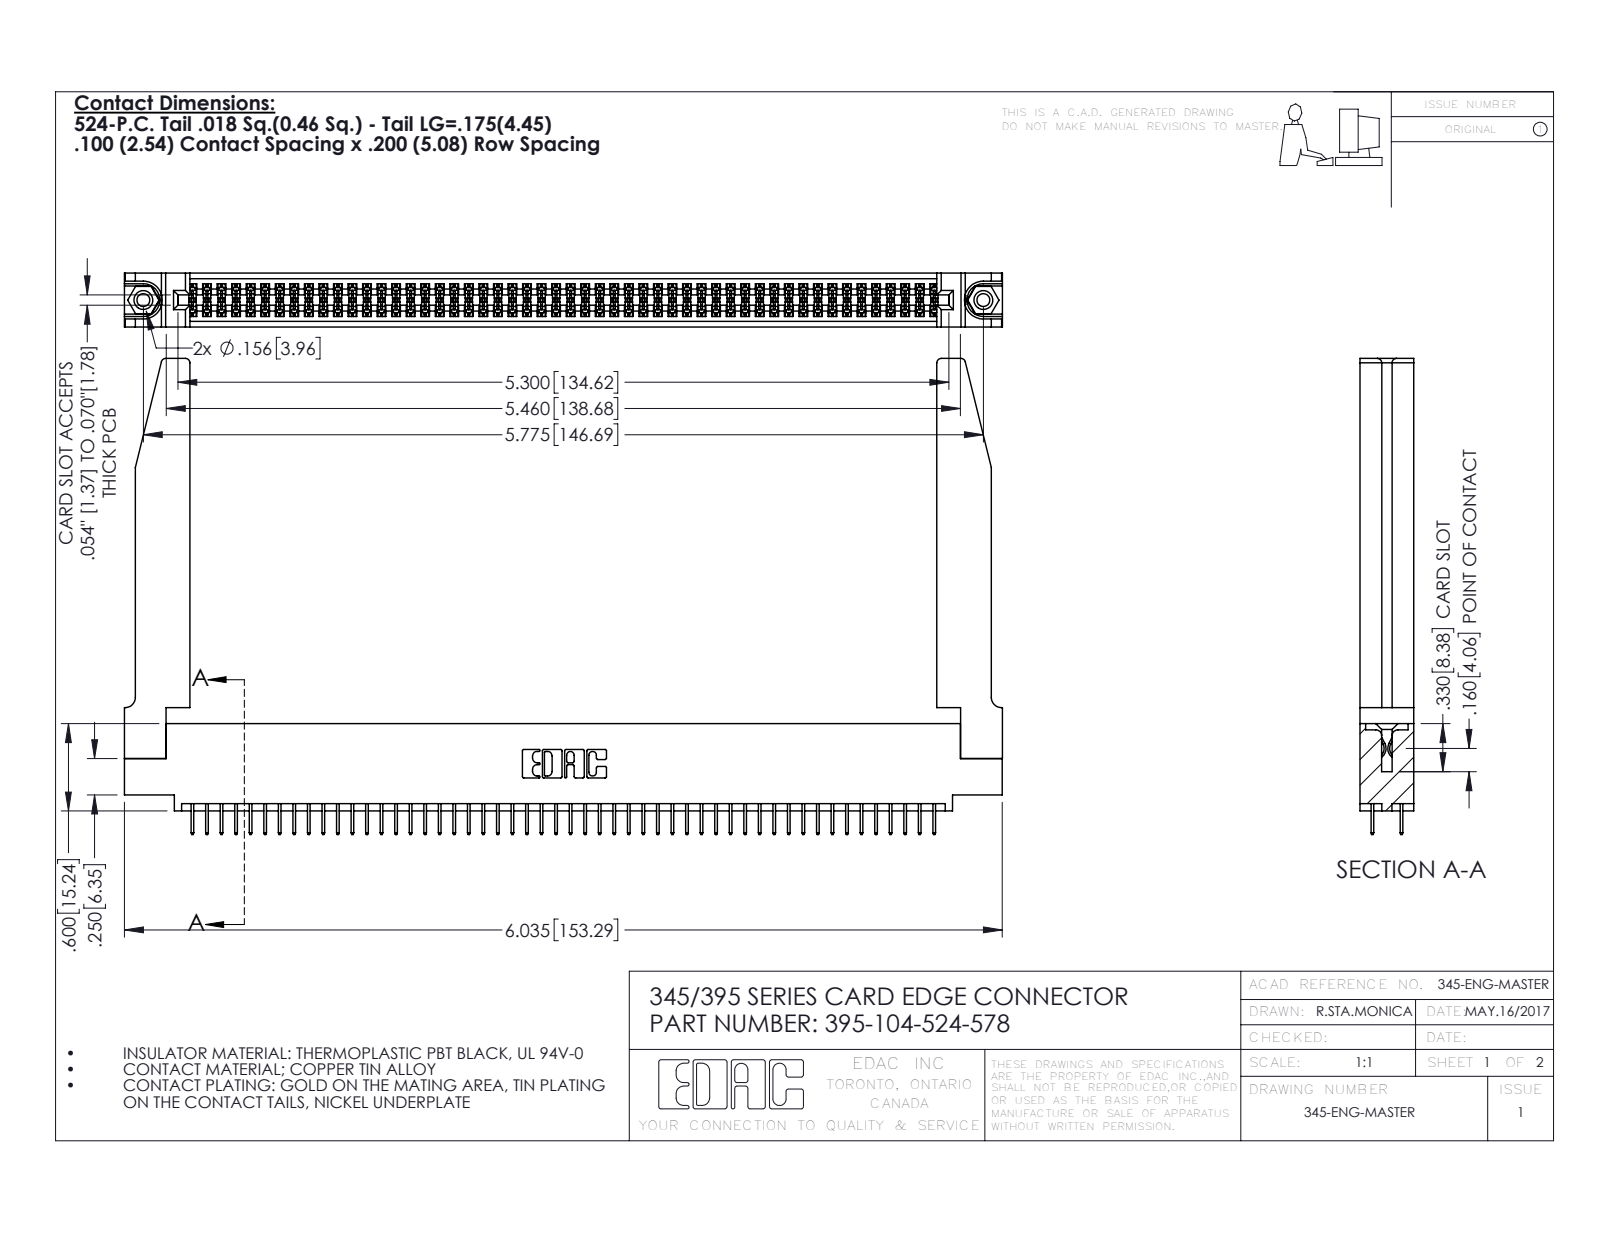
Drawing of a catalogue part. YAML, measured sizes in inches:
part_name: "345-250-001_345-250-001-102; 345-292-001_345-293-124; 345-220-078_345-220-078; 395-104-524-578 (+1 more)"
step_written_by: "SolidWorks 2016 (CONFIG_CONTROL_DESIGN)"
units: inches
bodies: {solids: 109, faces: 5980, planar: 4282, cylindrical: 1646, other: 52}
overall_size: [6.036, 3.272, 0.37]
volume: 1.375
surface_area: 44.21
round_holes:
  - {diameter: 0.089, count: 2}
  - {diameter: 0.125, count: 2}
  - {diameter: 0.156, count: 2}
  - {diameter: 0.064, count: 1}
round_bosses_or_shafts:
  - {diameter: 0.155, count: 2}
partial_cylinders:
  - {radius: 0.006, count: 156}
  - {radius: 0.01, count: 22}
  - {radius: 0.03, count: 8}
  - {radius: 0.007, count: 6}
  - {radius: 0.031, count: 6}
  - {radius: 0.026, count: 3}
  - {radius: 0.014, count: 2}
  - {radius: 0.019, count: 2}
face_to_face_distances: [0.072, 0.37, 0.298, 0.2, 0.098, 0.272, 0.025, 0.225, 0.072, 0.15]
hole_center_spacings: [0.27, 5.539, 5.775]
